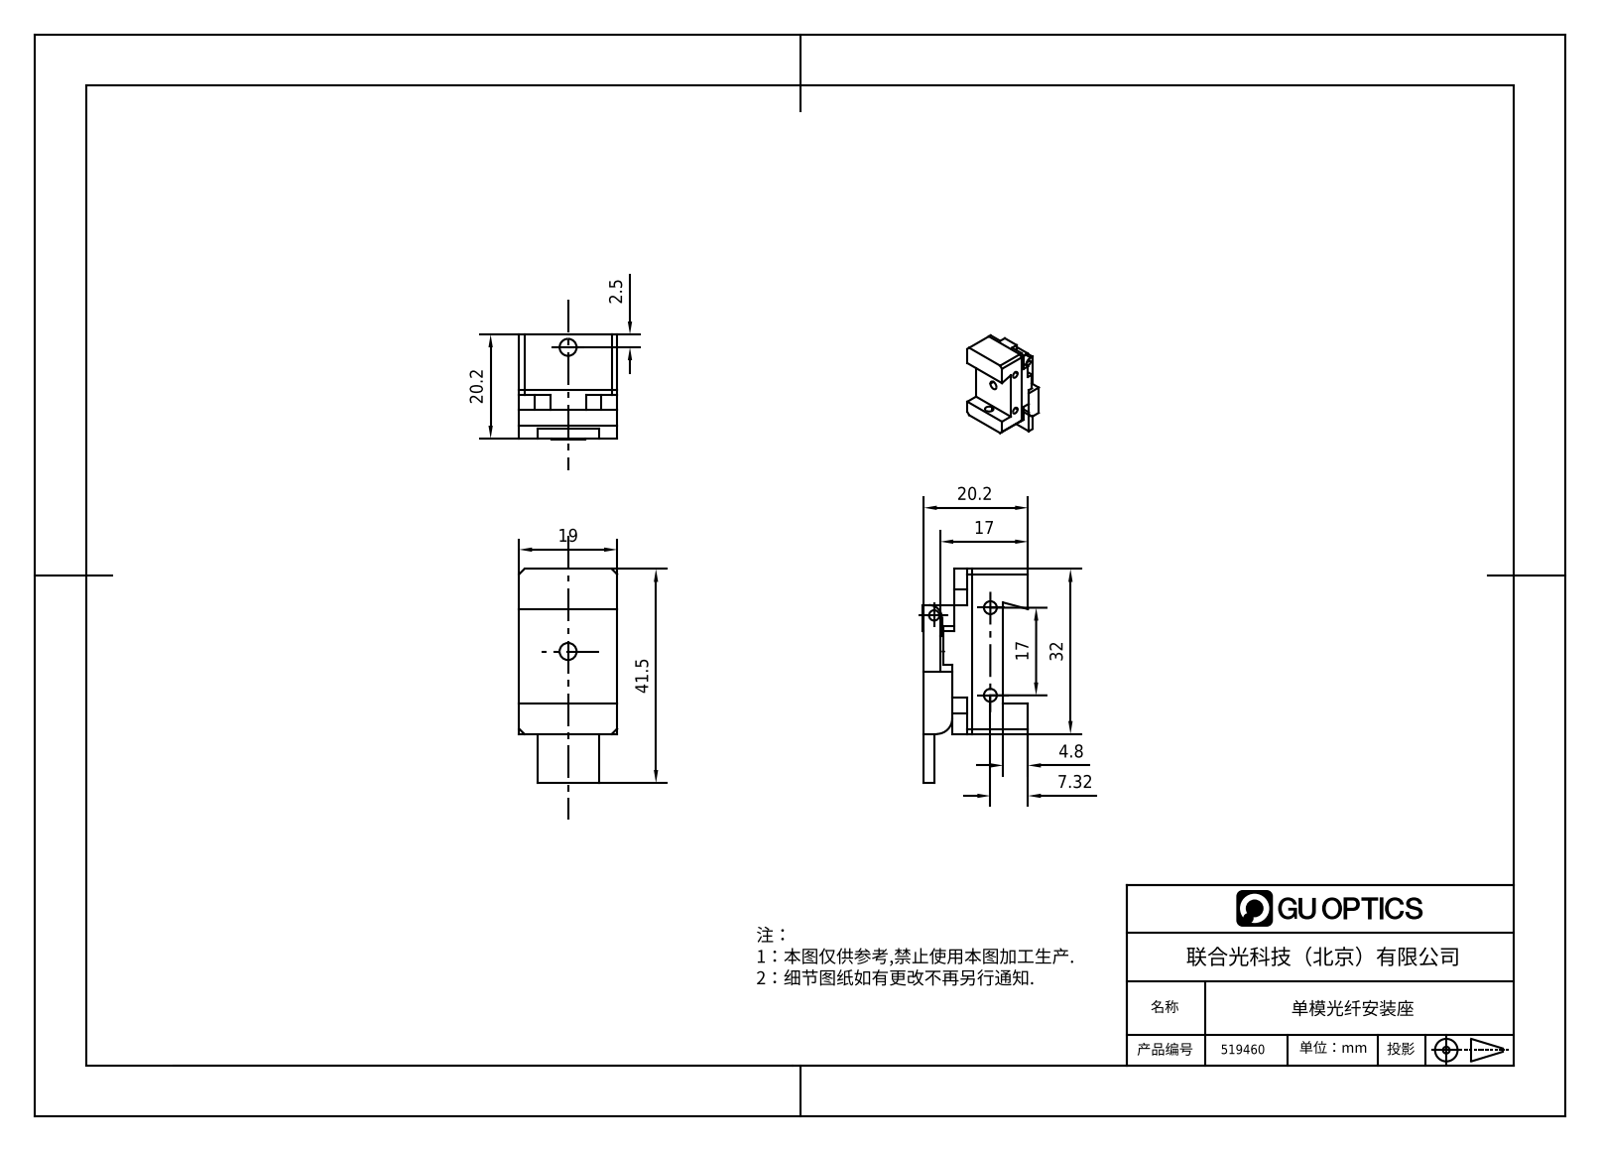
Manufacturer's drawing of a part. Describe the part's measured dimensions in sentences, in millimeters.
The part is named "SMF-FH". Its 3-D file was written by "SolidWorks 2016 (CONFIG_CONTROL_DESIGN)". It is 3 solids with 139 faces: 72 planar, 47 cylindrical and 20 other. Overall it measures 41.5 by 20.4 by 19 millimeters. Its volume is 8 270 cubic millimeters and its surface area 6 136 square millimeters. Round holes: 6 of diameter 2.5, 4 of diameter 3.5, 2 of diameter 3.3, 1 of diameter 1.6, 1 of diameter 2, 1 of diameter 6. Partial cylindrical surfaces (rounded edges, fillets, slot ends): 5 of radius 3, 2 of radius 1, 1 of radius 2.5. The main face-to-face distances are 9.4, 3.9, 6, 19, 15.4, 3.5, 5.5, 9.9, 20.2, 14.7. The hole center spacings are 14.02, 7.78, 8.74, 12.7, 20.03, 21.46, 25, 28.04.
